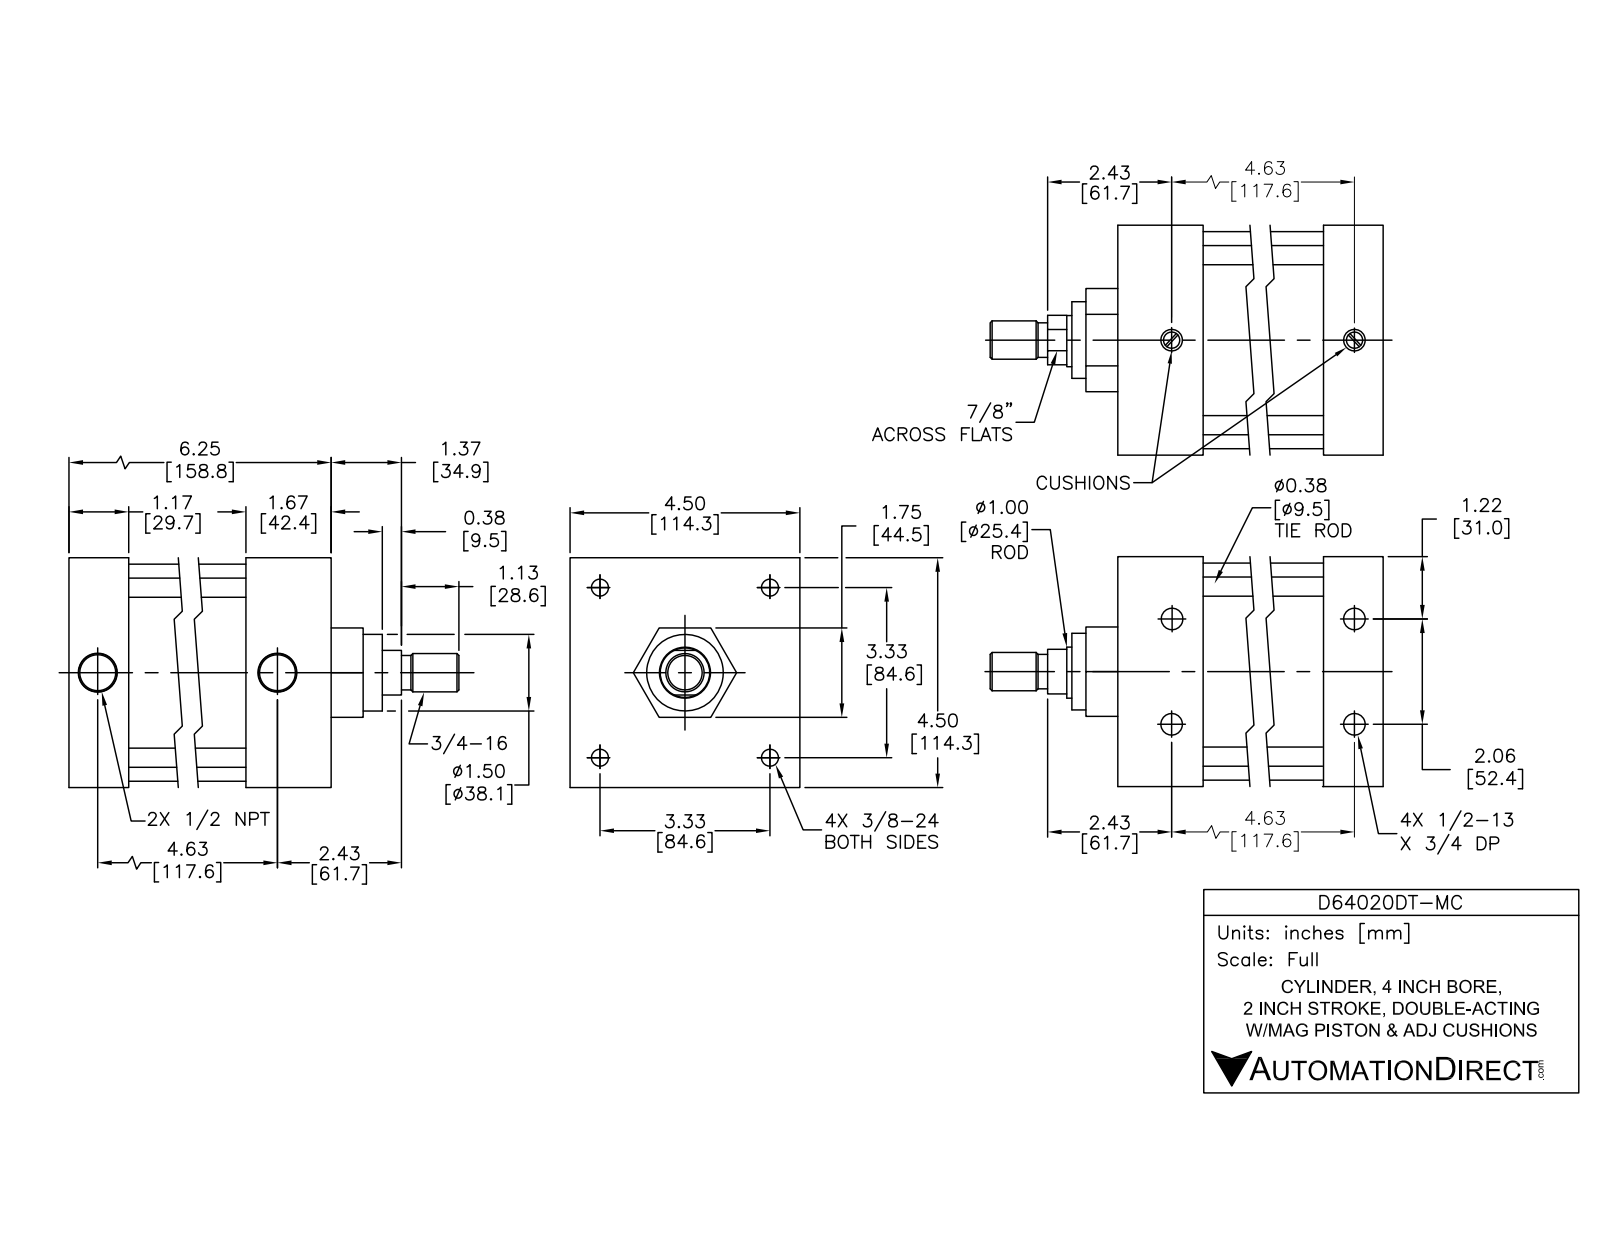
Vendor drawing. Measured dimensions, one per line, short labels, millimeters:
name: D64020DT-M BODY; D64020DT-M PISTON; D64020DT-MC
written by: SolidWorks 2015 (AUTOMOTIVE_DESIGN)
unit: mm
bodies: 12 solids, 303 faces (99 planar, 114 cylindrical, 90 other)
size: 222.1 × 114.3 × 114.3
volume: 1 358 000 mm³; area: 230 300 mm²
holes: 4× ⌀8.4, 4× ⌀10.3, 4× ⌀10.6, 4× ⌀15.9, 2× ⌀12.7, 2× ⌀19.5, 1× ⌀25.4, 1× ⌀25.5, 1× ⌀101.6
bosses: 4× ⌀15.5, 4× ⌀9.5, 4× ⌀8.6, 1× ⌀108, 1× ⌀101.5, 1× ⌀44.5, 1× ⌀25.3, 1× ⌀24.6
rounds: 4× R11.4
face distances: 114.3, 2, 84.5, 158.6, 44.5, 126.9, 31.7, 95.3, 31.6, 63.4
hole spacings: 26.2, 120.3, 117.4, 52.4, 59.7, 59.7, 84.4, 84.4
